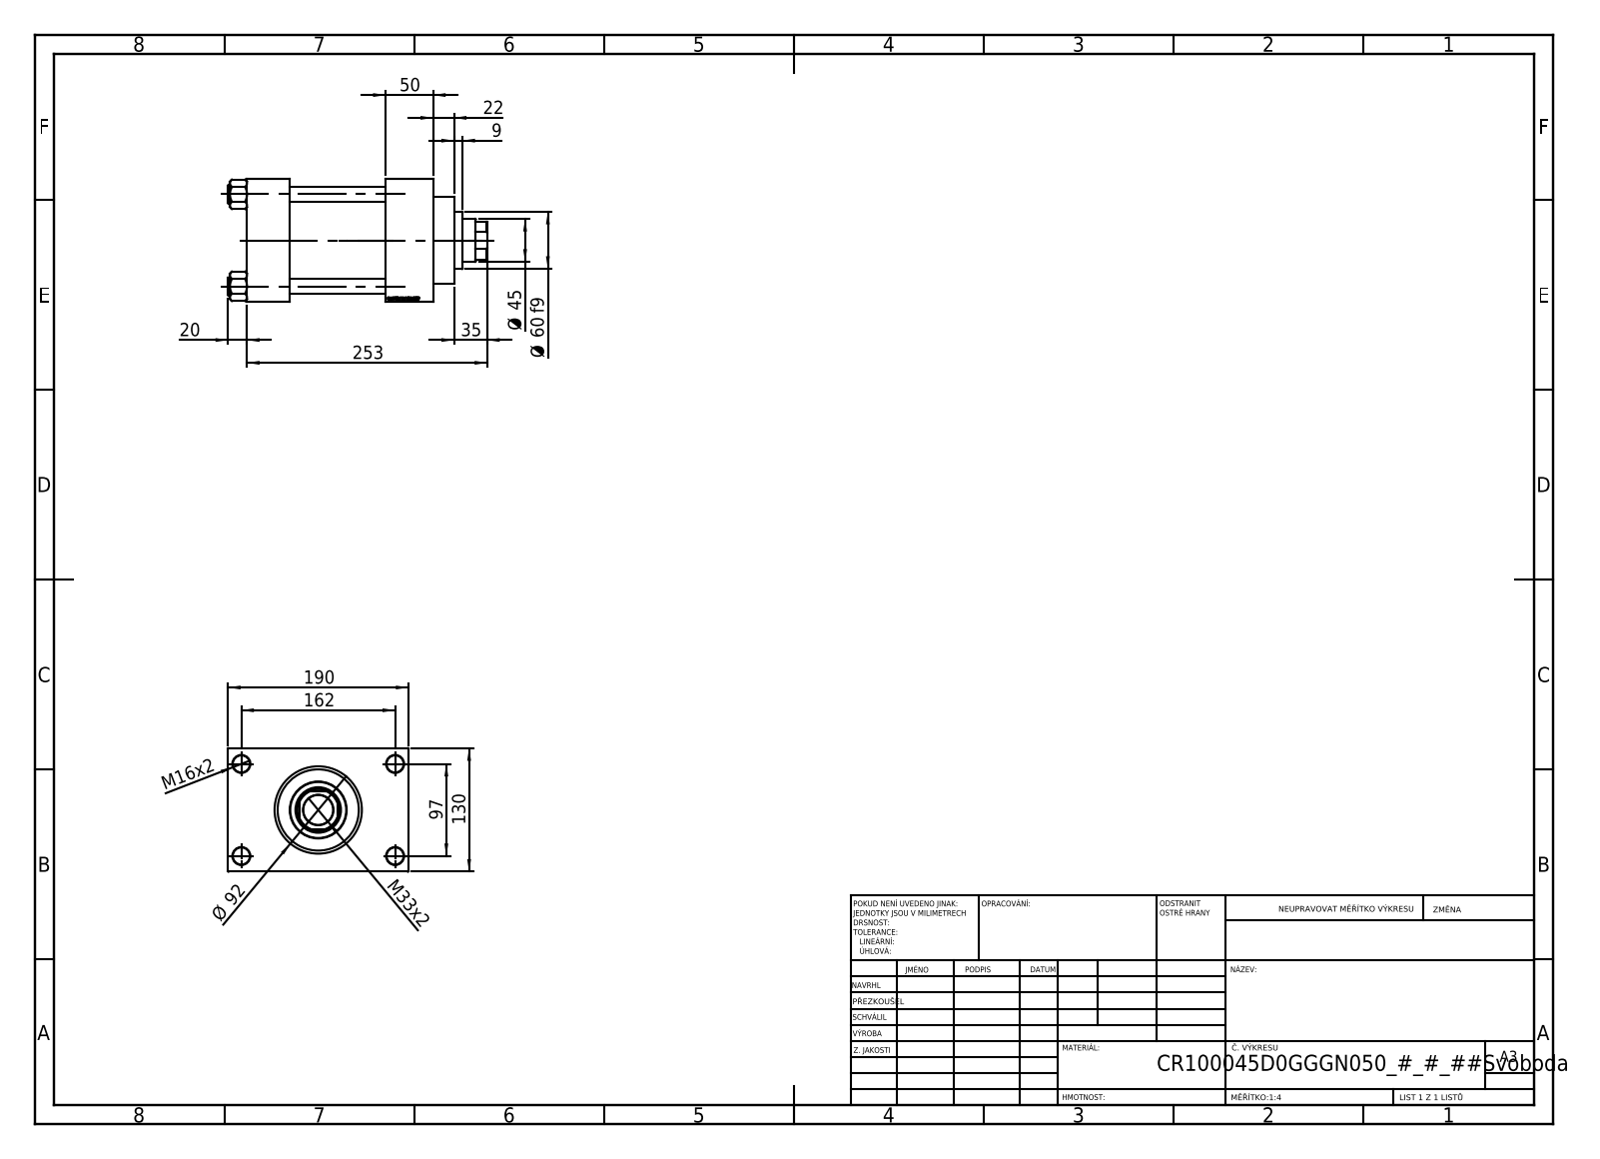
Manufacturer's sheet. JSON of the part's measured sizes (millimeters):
{"part_name": "NUT_M5_D; V215CR_VCP_D; V215CR_D_TYCINKA; V215_VC_A (+1 more)", "step_written_by": "SolidWorks 2019 (CONFIG_CONTROL_DESIGN)", "units": "millimeters", "bodies": {"solids": 11, "faces": 1152, "planar": 545, "cylindrical": 89, "other": 518}, "overall_size": [273, 190, 130], "volume_mm3": 2708000, "surface_area_mm2": 382082, "round_holes": [[16, 4], [18, 4], [7, 2], [26.44, 2], [35, 2], [31.5, 1], [45, 1], [48, 1], [76, 1], [85.5, 1], [100, 1]], "round_bosses_or_shafts": [[19, 4], [106, 1], [92, 1], [60, 1]], "partial_cylinders_radius": [[22, 1]], "face_to_face_distances": [50, 130, 45, 146, 101, 196, 151, 30, 160, 190], "hole_center_spacings": [32.55, 68.52, 94.41, 96.9, 102.27, 129.45, 161.73, 97]}
